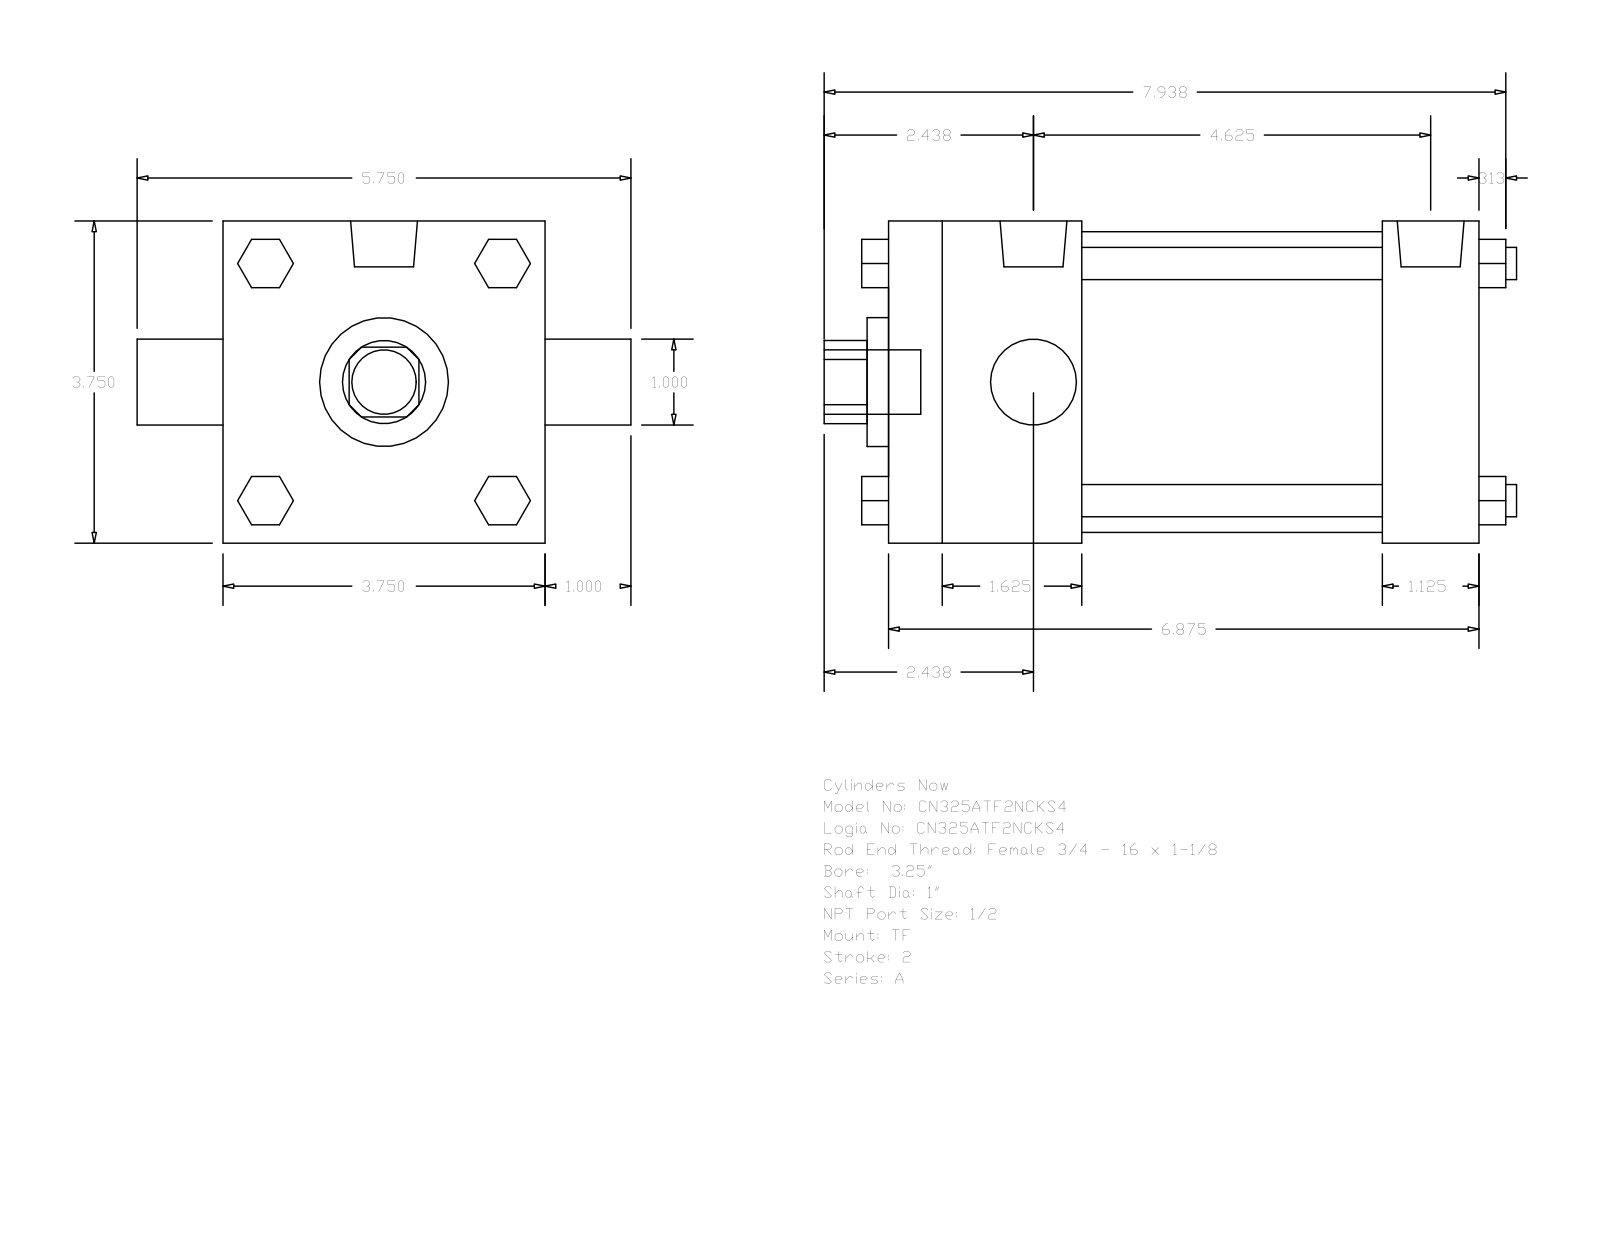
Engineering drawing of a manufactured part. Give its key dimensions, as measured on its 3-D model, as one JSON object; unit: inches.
{"part_name": "A_TF__0325_1", "step_written_by": "GSSL Pune (CONFIG_CONTROL_DESIGN)", "units": "inches", "bodies": {"solids": 0, "faces": 120, "planar": 92, "cylindrical": 28, "other": 0}, "overall_size": [8.063, 5.75, 3.75], "round_holes": [[1, 2], [1.5, 1], [3.5, 1]], "round_bosses_or_shafts": [[0.375, 4], [0.344, 3], [0.778, 2], [0.75, 1]], "partial_cylinders_radius": [[0.484, 1]], "face_to_face_distances": [3.75, 6.875, 2.25, 5.75, 3.5, 4.625, 1.125, 0.562, 1.38, 2.39]}
